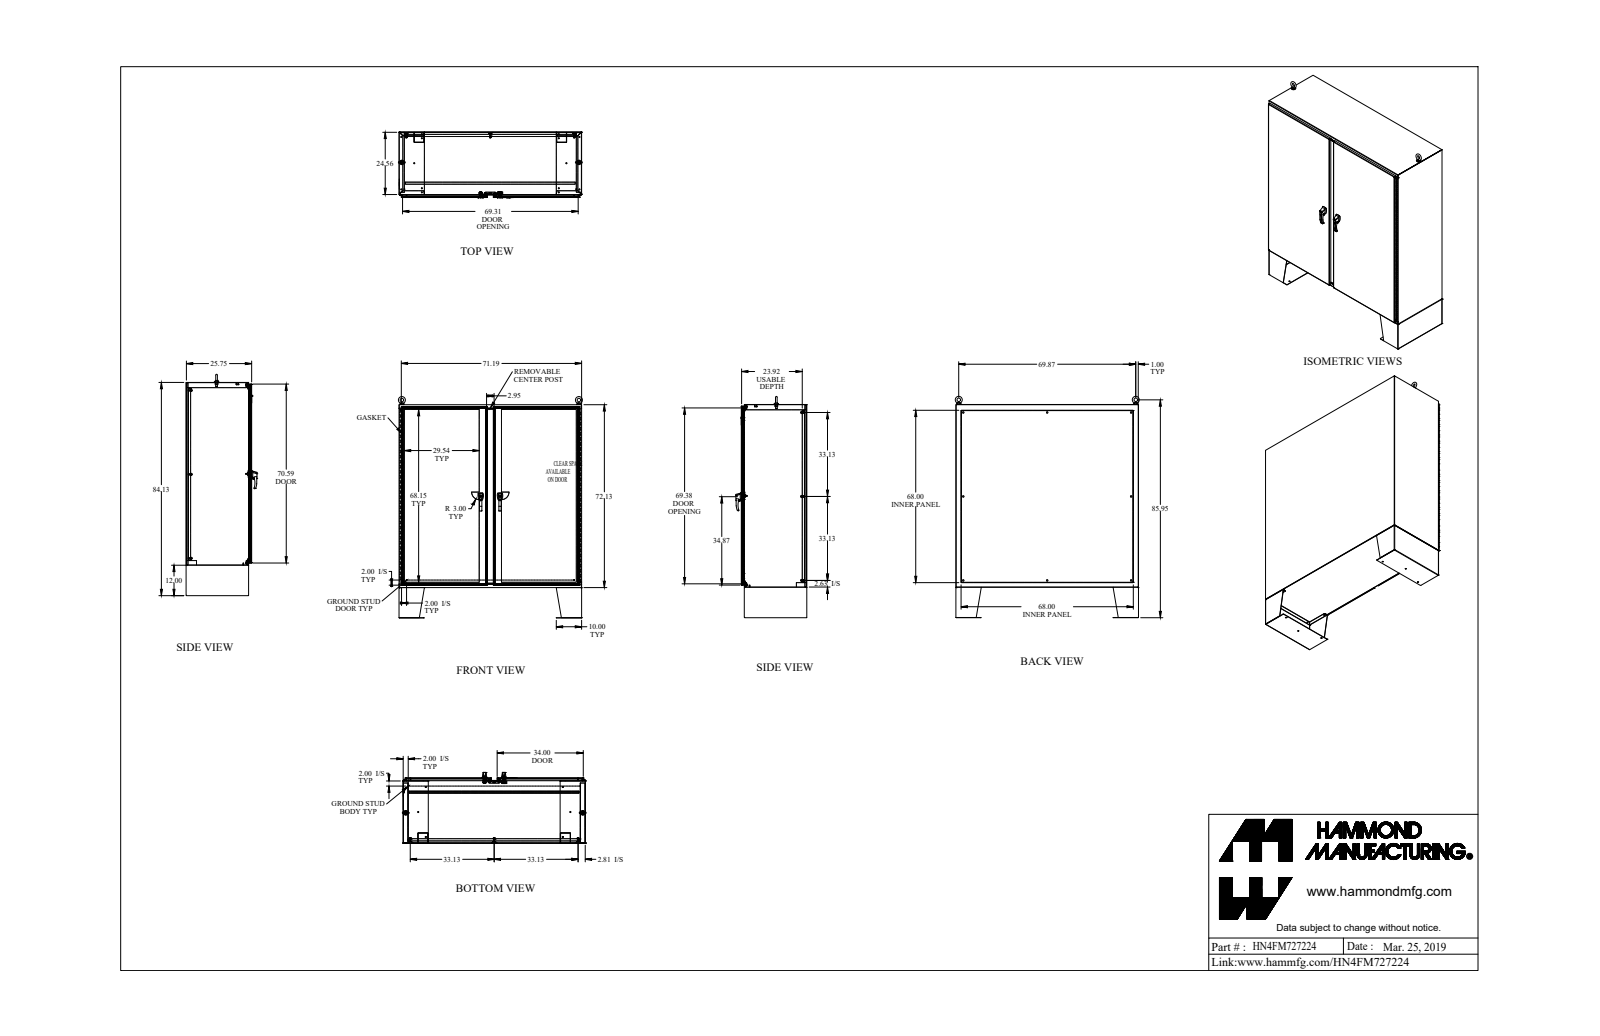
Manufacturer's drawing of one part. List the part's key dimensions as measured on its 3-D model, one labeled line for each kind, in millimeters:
Part name (STEP PRODUCT): HN4FM727224
STEP written by: SolidWorks 2018 (AUTOMOTIVE_DESIGN)
Units: millimetres
Bodies: 132 solids, 3996 faces (1828 planar, 1795 cylindrical, 373 other)
Overall size (bounding box): 2217.8 × 1844.2 × 710.9
Volume: 47 560 000 mm³ · Surface area: 35 600 000 mm²
Round holes (diameter × count): ⌀7.7 ×24, ⌀11.1 ×14, ⌀7.8 ×8, ⌀8.9 ×8, ⌀14.3 ×8, ⌀6.4 ×6, ⌀11.3 ×6, ⌀7.1 ×4, ⌀7.1 ×4, ⌀8 ×4, ⌀9.9 ×4, ⌀10.5 ×4
Round bosses / shafts (diameter × count): ⌀25.4 ×12, ⌀16.5 ×8, ⌀9.5 ×8, ⌀8.4 ×8, ⌀7.1 ×8, ⌀6.4 ×6, ⌀16 ×5, ⌀19.1 ×4
Partial cylindrical surfaces — rounded edges, fillets, slot ends (radius × count): R12.7 ×33, R0.5 ×32, R3.2 ×32, R1.5 ×28, R1.2 ×27, R3.6 ×27, R0.8 ×12, R2.3 ×12
Main face-to-face distances: 2.4, 3.2, 42.8, 654.8, 651.6, 657.2, 654.1, 46, 608.8, 611.2
Hole centre spacings: 152.4, 304.8, 457.2, 609.6, 1881.4, 762, 914.4, 1682.8
